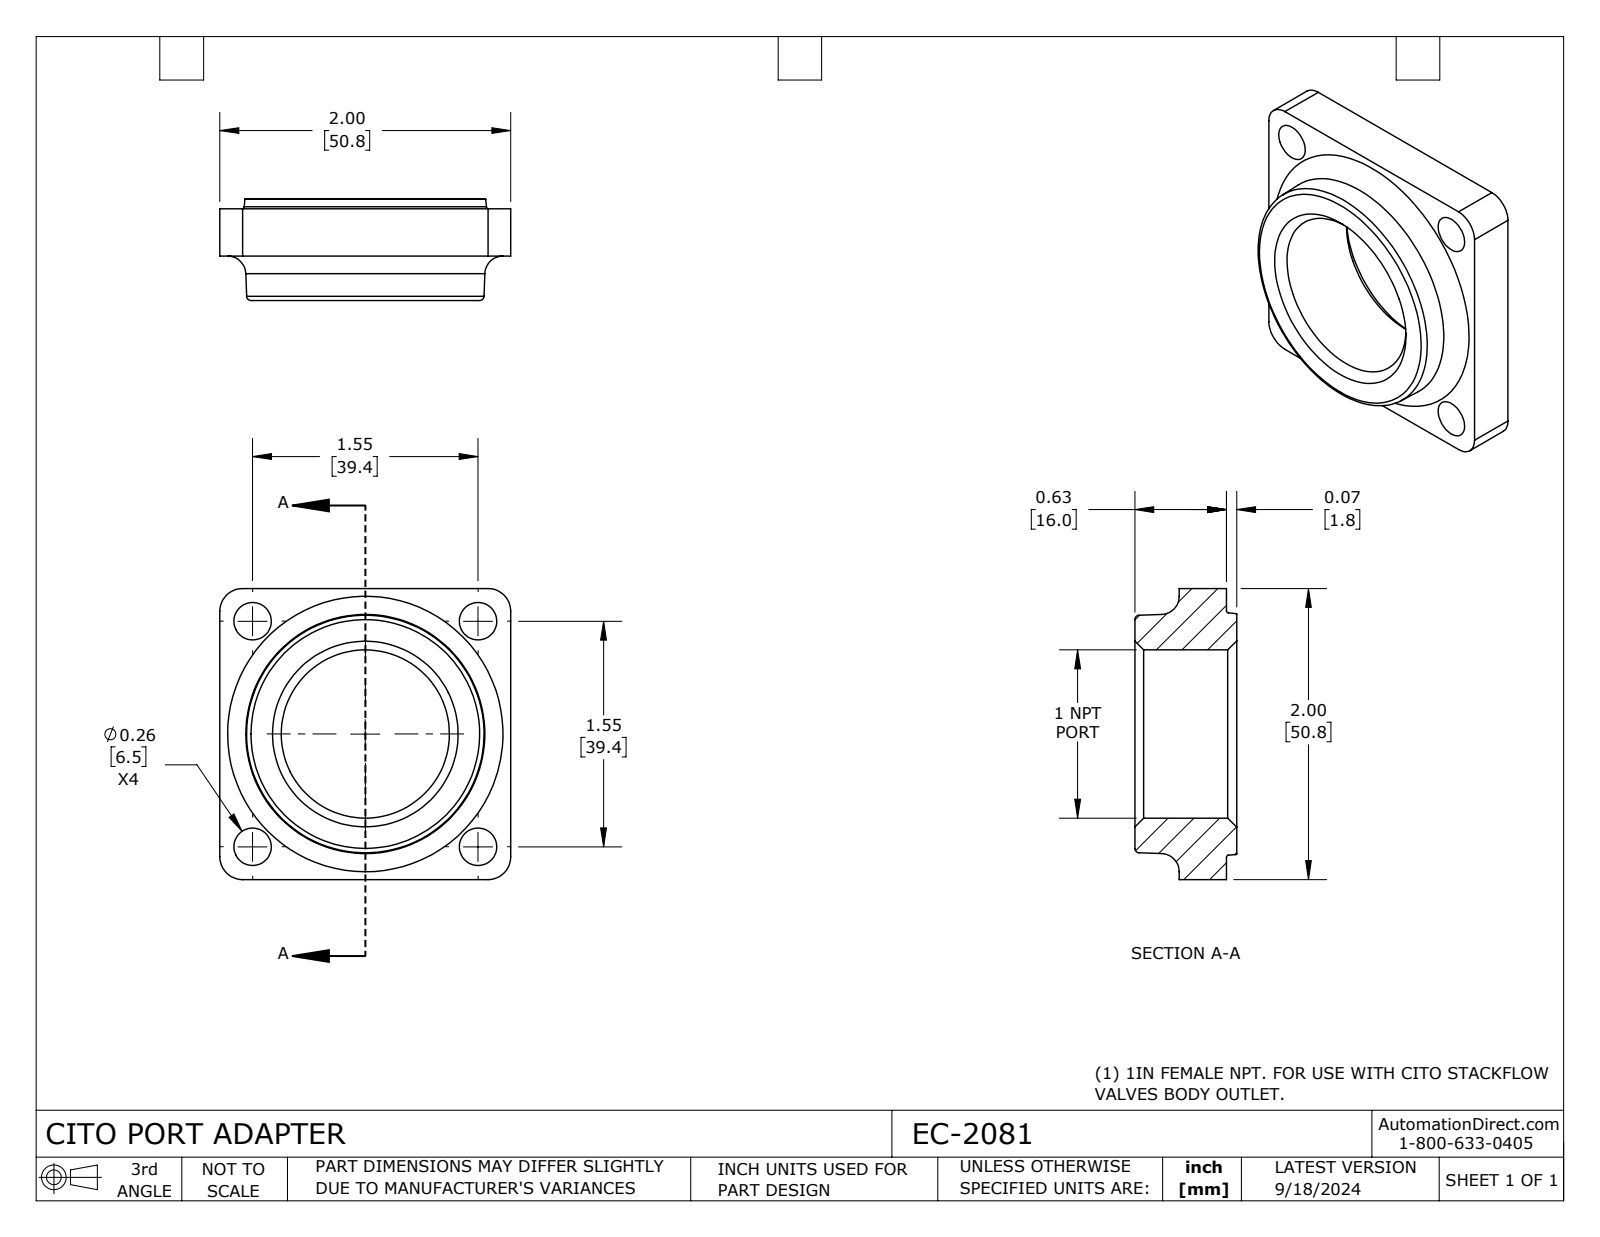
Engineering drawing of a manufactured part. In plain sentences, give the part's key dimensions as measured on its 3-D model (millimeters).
The part is named "EC-2081". Its 3-D file was written by "SolidWorks 2023 (CONFIG_CONTROL_DESIGN)". It is 1 solid with 39 faces: 8 planar, 15 cylindrical and 16 other. Overall it measures 50.8 by 50.8 by 17.8 millimeters. Its volume is 21 120 cubic millimeters and its surface area 8 258 square millimeters. Round holes: 4 of diameter 6.5, 1 of diameter 29.4. Partial cylindrical surfaces (rounded edges, fillets, slot ends): 4 of radius 4. The main face-to-face distances are 50.8, 8.3, 10, 1.8, 7.7, 16, 17.8. The hole center spacings are 27.8, 39.4, 27.8, 39.4, 55.7, 55.7.
